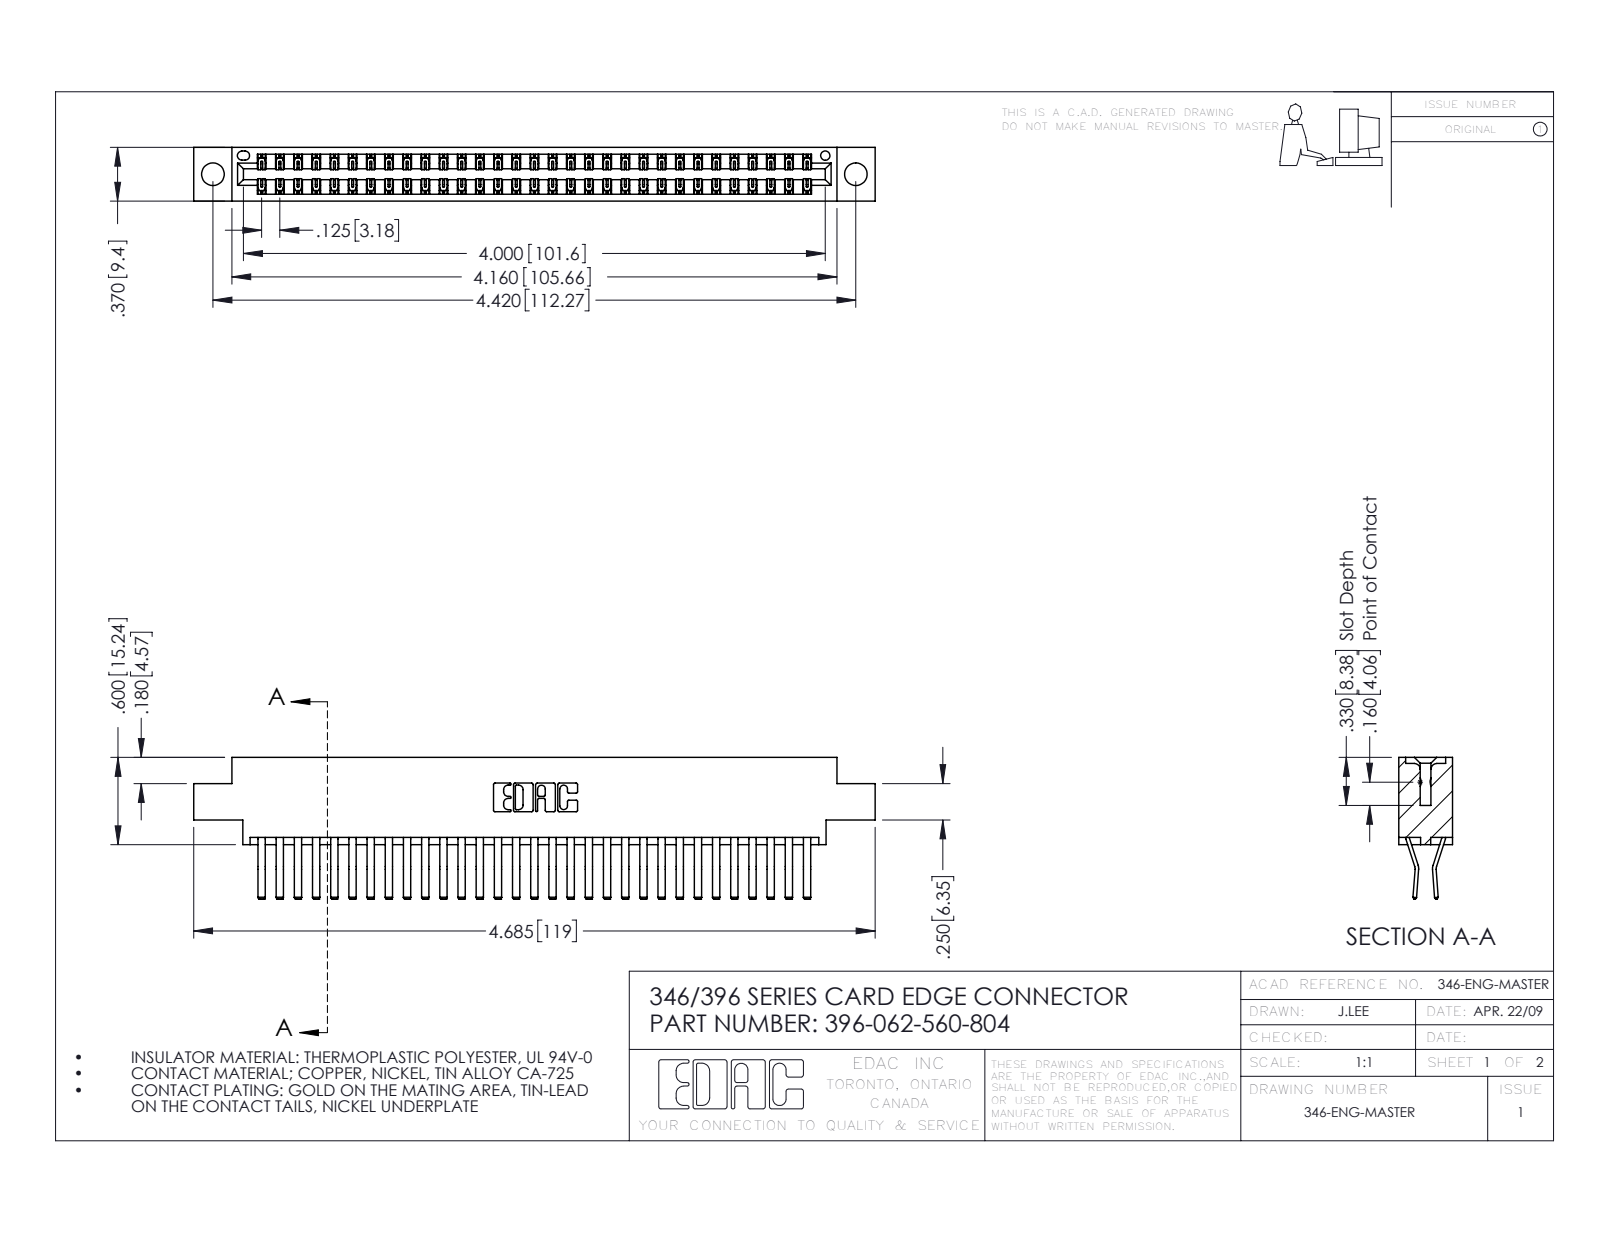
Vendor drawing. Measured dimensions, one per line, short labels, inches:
name: 396-062-560-804; 346 Part_0.170 Offset - 0.156 Dia-TH; 345-292-001_560 Tail
written by: SolidWorks 2016 (CONFIG_CONTROL_DESIGN)
unit: in
bodies: 63 solids, 3474 faces (2250 planar, 1224 cylindrical, 0 other)
size: 4.685 × 0.975 × 0.37
volume: 0.713 in³; area: 26.29 in²
holes: 2× ⌀0.156, 1× ⌀0.064
rounds: 93× R0.006, 22× R0.01, 6× R0.007, 6× R0.031, 3× R0.026, 2× R0.01, 2× R0.014, 2× R0.022
face distances: 0.048, 0.322, 0.37, 0.025, 0.25, 0.072, 0.298, 0.275, 0.148, 0.222
hole spacings: 0.246, 4.212, 4.42
